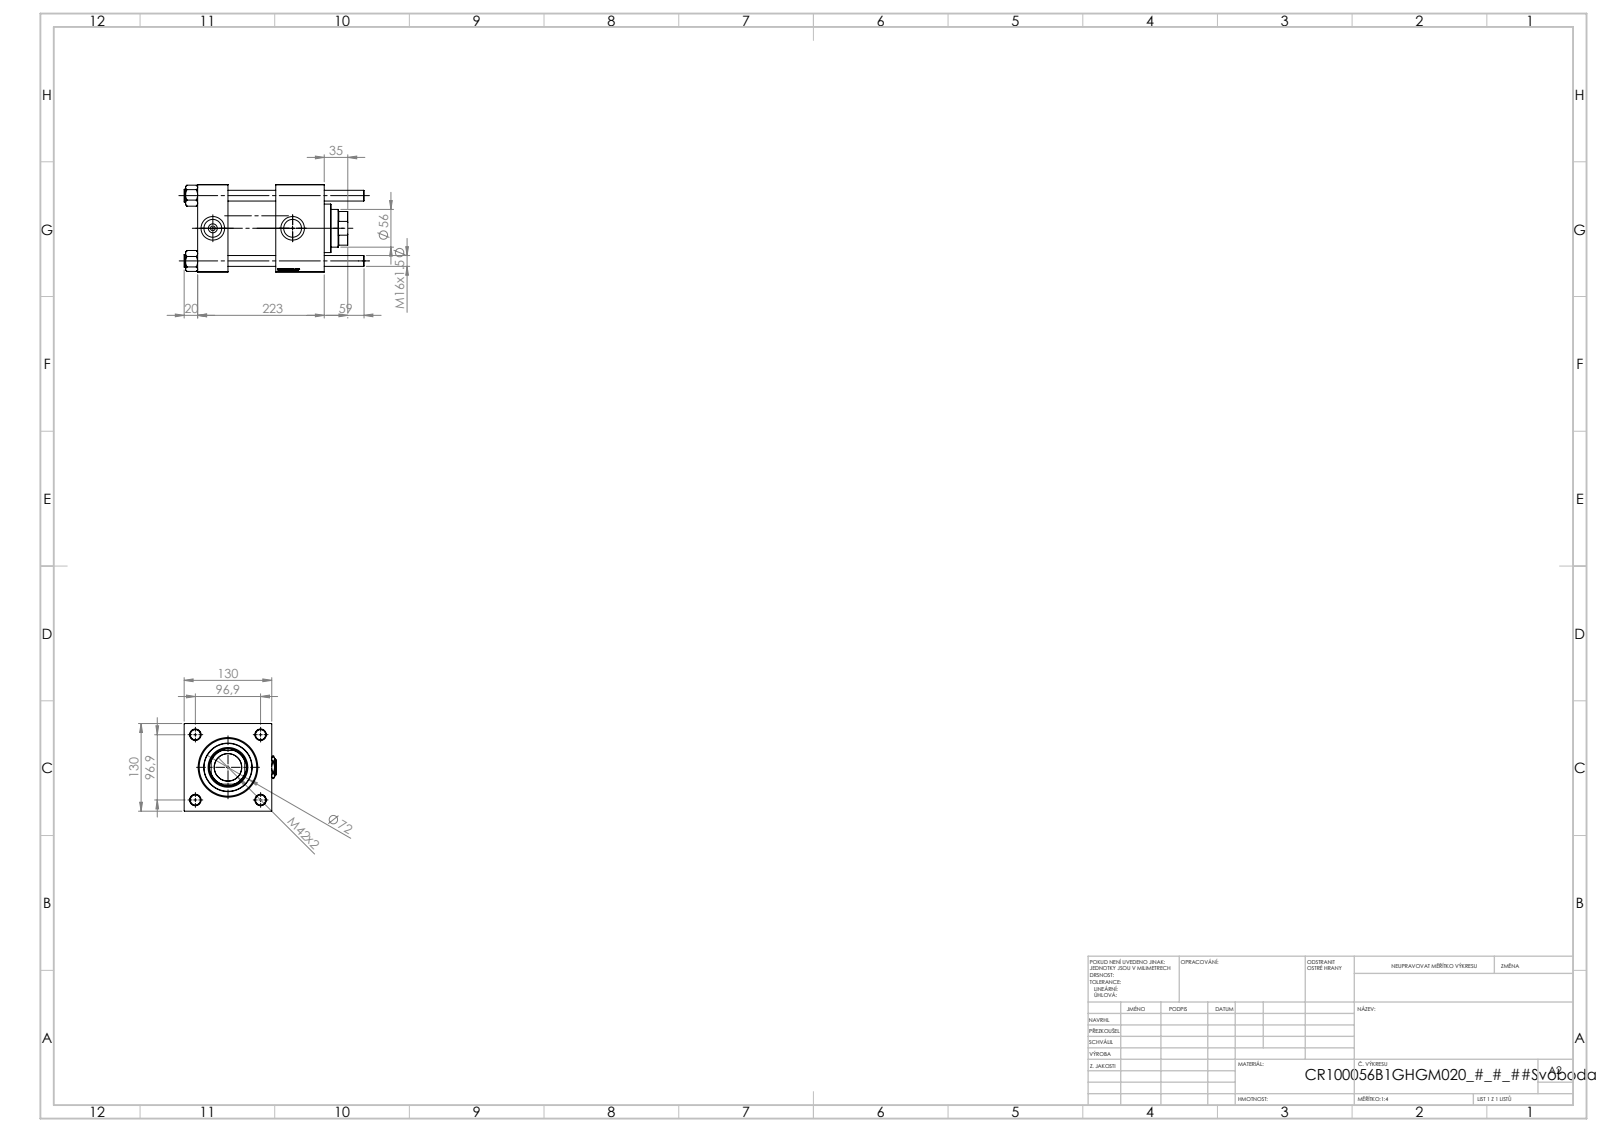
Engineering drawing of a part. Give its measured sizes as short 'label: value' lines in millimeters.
name: V215CR_B_TYCINKA; NUT_M5_B; V215CR_B-1; V215CR_VCP_B (+2 more)
written by: SolidWorks 2019 (CONFIG_CONTROL_DESIGN)
unit: mm
bodies: 12 solids, 1253 faces (503 planar, 82 cylindrical, 668 other)
size: 267 × 137 × 130
volume: 2 544 000 mm³; area: 363 595 mm²
holes: 4× ⌀16, 2× ⌀7, 2× ⌀26.44, 2× ⌀35, 1× ⌀40.5, 1× ⌀56, 1× ⌀59, 1× ⌀76, 1× ⌀85.5, 1× ⌀100
bosses: 4× ⌀19, 1× ⌀106, 1× ⌀72
rounds: 1× R27
face distances: 130, 45, 188, 143, 116, 71, 72, 20, 51, 96
hole spacings: 68.52, 96.9, 137.04, 118.5
